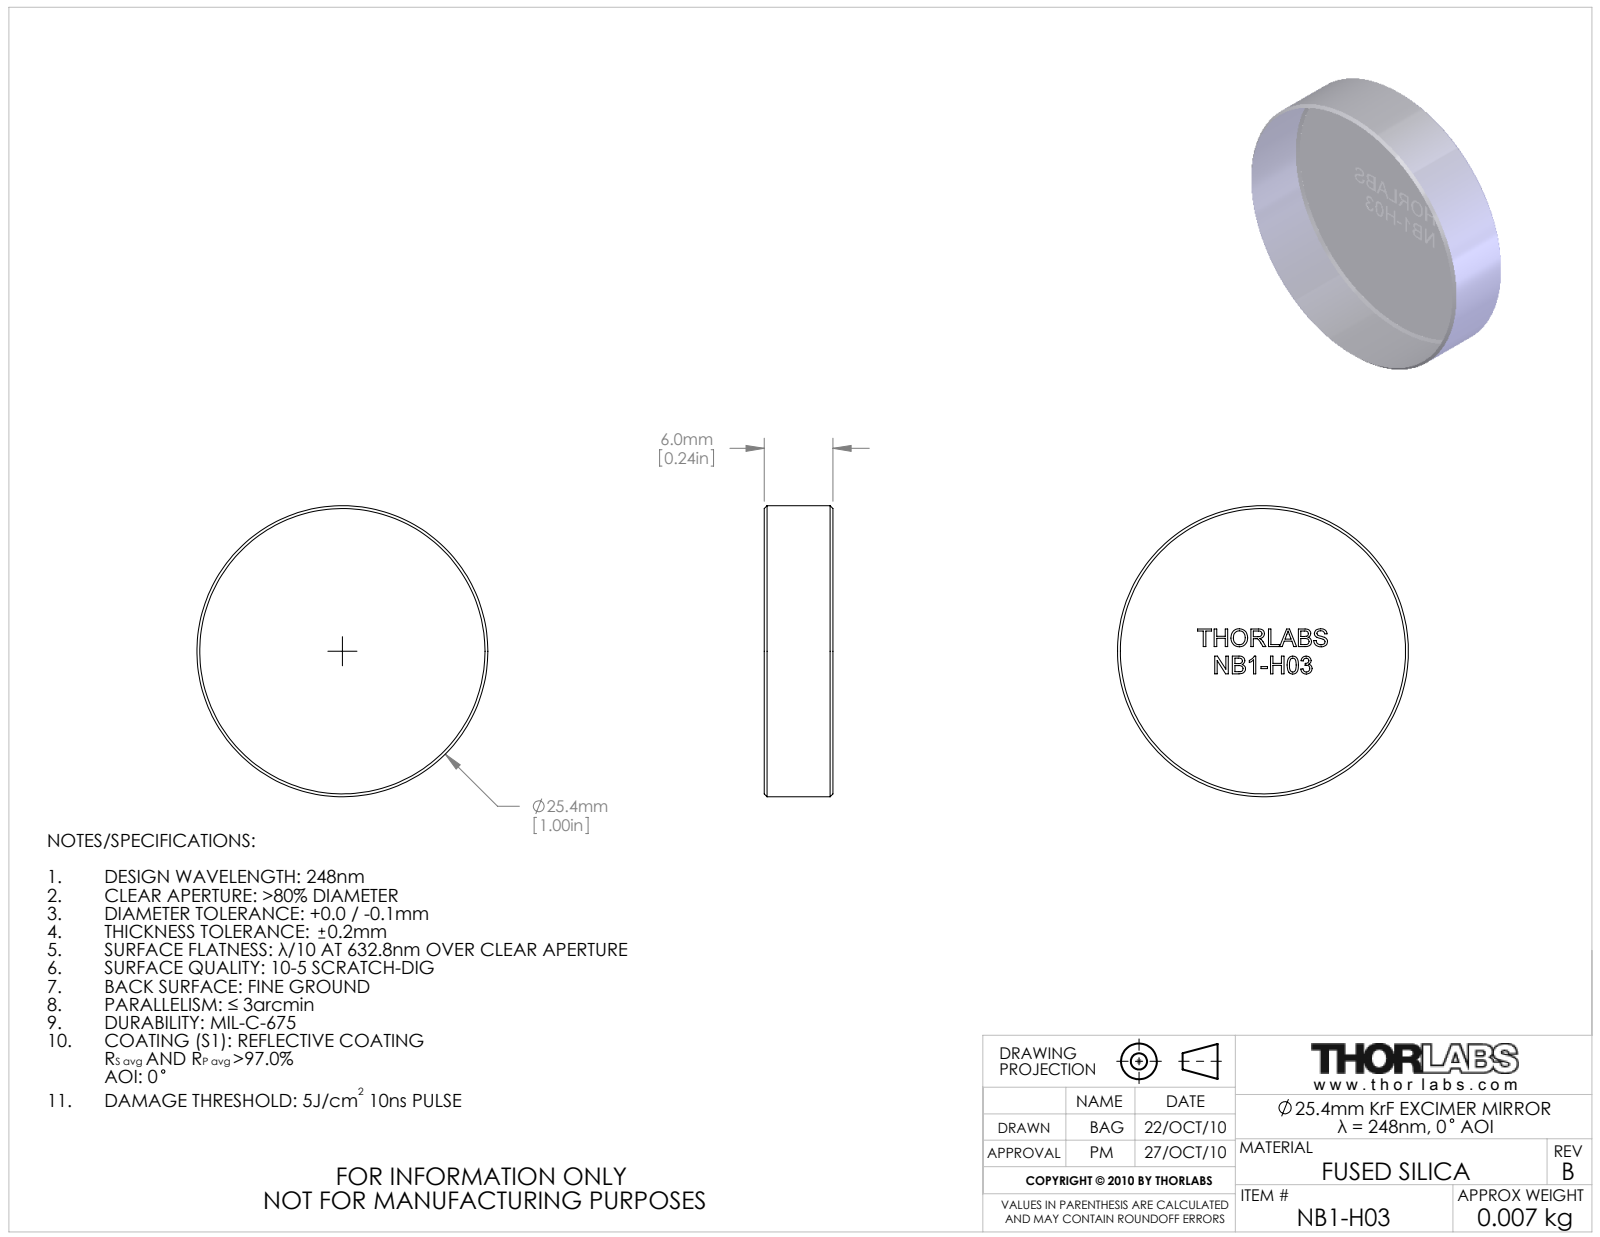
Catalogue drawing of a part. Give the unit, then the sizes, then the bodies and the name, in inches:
Units: inches
Overall size (bounding box): 1 × 1 × 0.236
Round bosses / shafts (diameter × count): ⌀1 ×1
Main face-to-face distances: 0.236, 0.061, 0.193, 0.093, 0.086, 0.038, 0.054, 0.094, 0.047, 0.146
Volume: 0.185 in³ · Surface area: 2.276 in²
Bodies: 1 solid, 211 faces (127 planar, 2 cylindrical, 82 other)
Part name (STEP PRODUCT): 5378-E0W
STEP written by: SolidWorks 2009 (AUTOMOTIVE_DESIGN)
